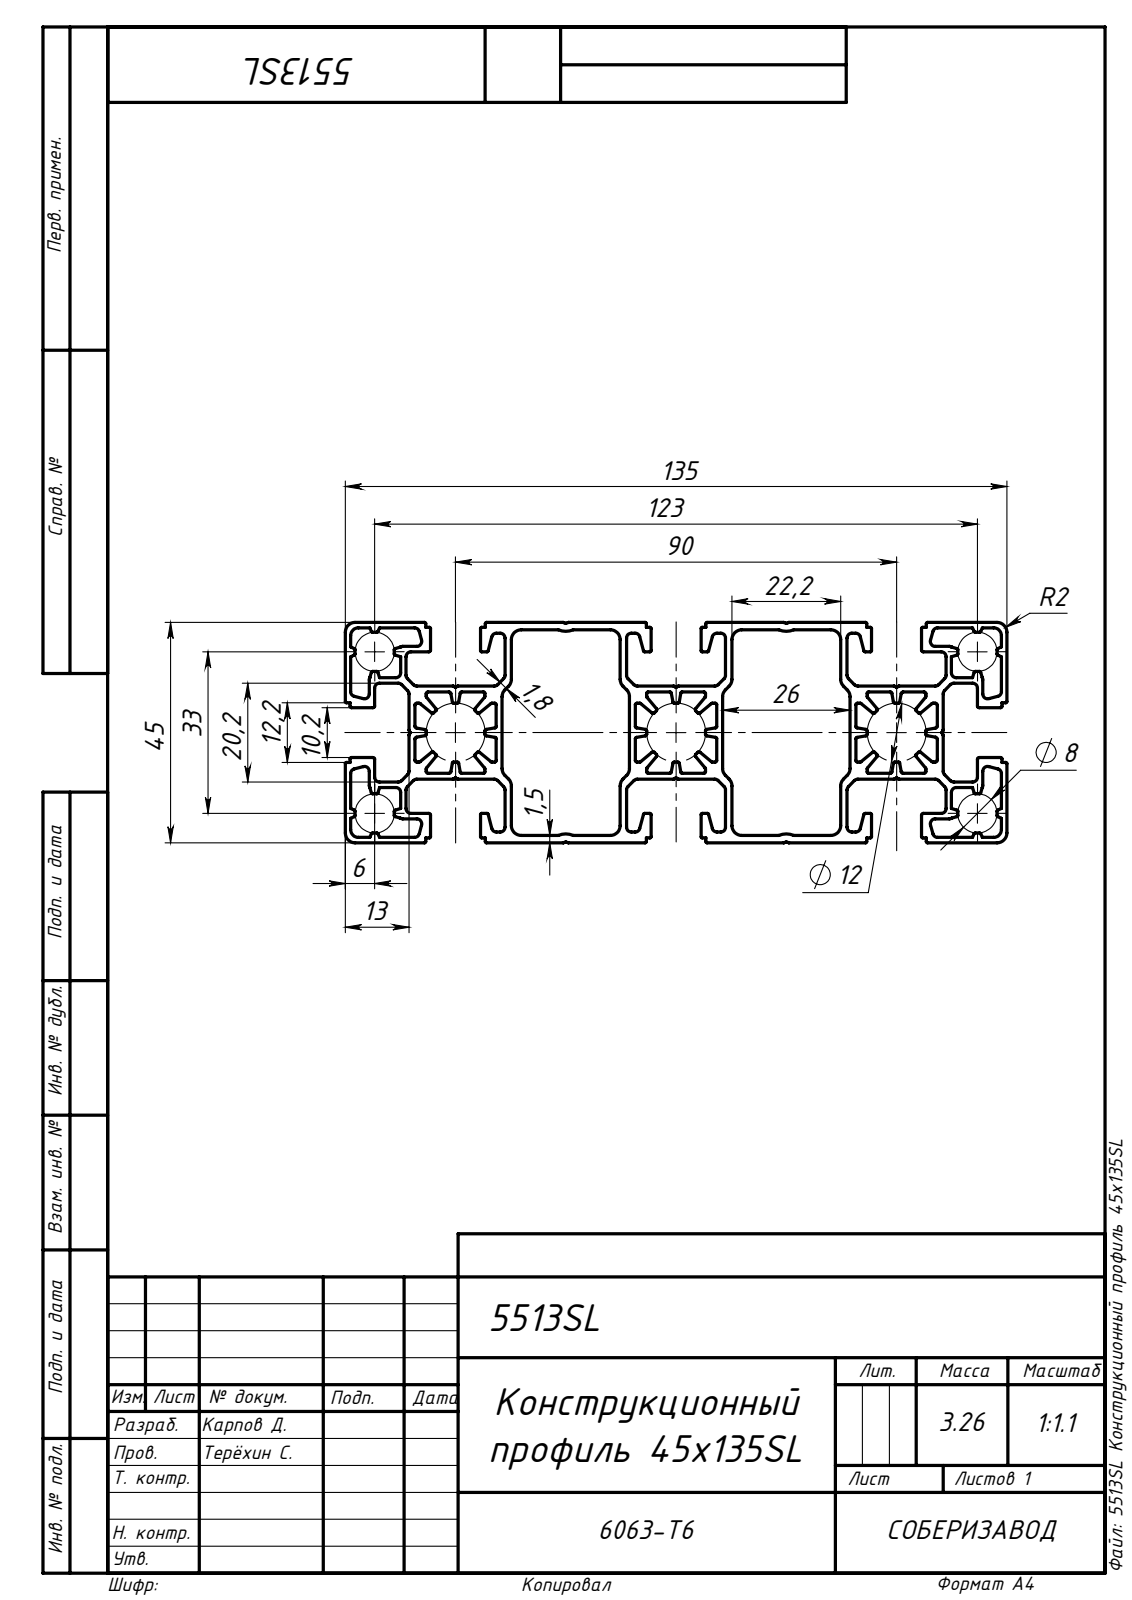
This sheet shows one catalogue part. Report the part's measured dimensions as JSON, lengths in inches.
{"step_written_by": "SolidWorks 2019 (AUTOMOTIVE_DESIGN)", "units": "inches", "bodies": {"solids": 1, "faces": 774, "planar": 406, "cylindrical": 368, "other": 0}, "overall_size": [39.37, 5.315, 1.772], "volume_in3": 73.59, "surface_area_in2": 2395, "partial_cylinders_radius": [[0.01, 120], [0.039, 92], [0.012, 80], [0.079, 28], [0.016, 24], [0.014, 8], [0.063, 4], [0.157, 4]], "face_to_face_distances": [1.772, 0.512, 1.26, 0.043, 0.748, 0.772, 0.024, 0.469, 1.217, 0.051]}
